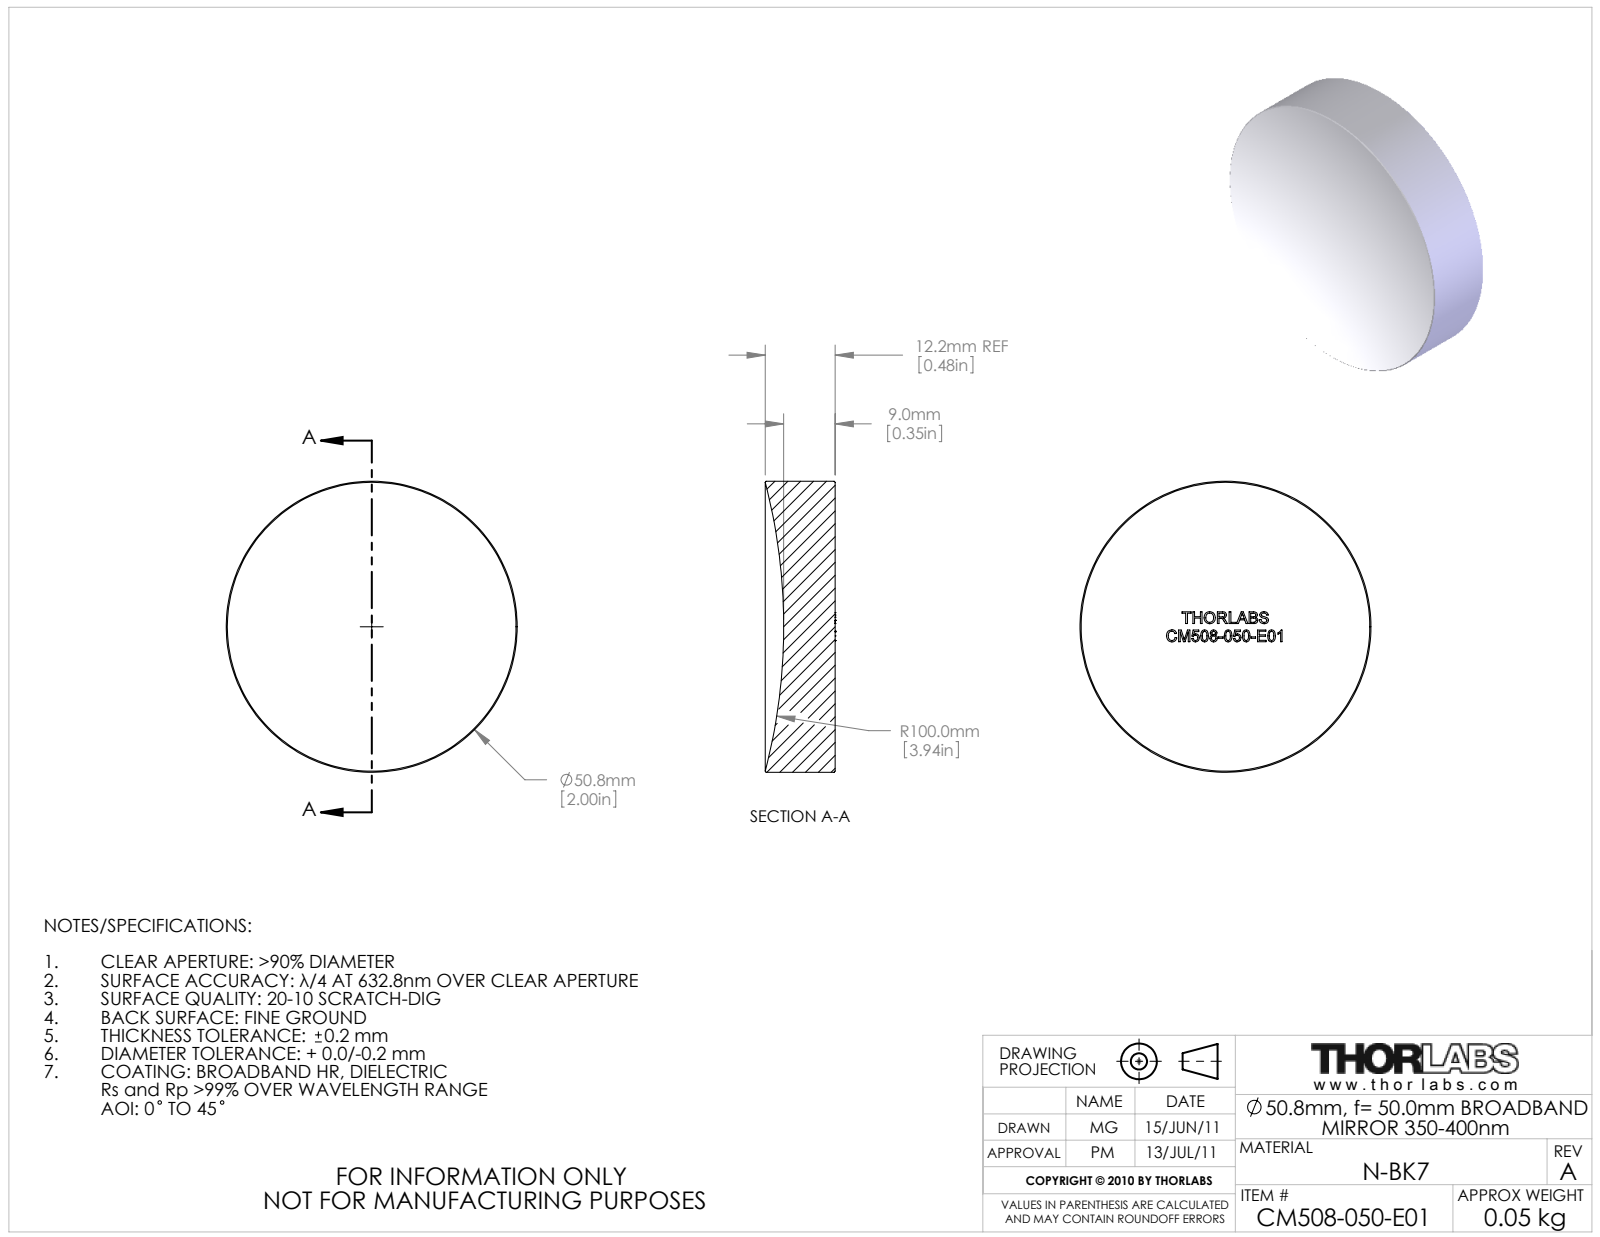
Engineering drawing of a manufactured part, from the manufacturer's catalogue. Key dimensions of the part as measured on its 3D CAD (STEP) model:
Part name (STEP PRODUCT): 22615-E0W
STEP written by: SolidWorks 2011 (AUTOMOTIVE_DESIGN)
Units: millimetres
Bodies: 0 solids, 43 faces (35 planar, 2 cylindrical, 6 other)
Overall size (bounding box): 50.8 × 50.8 × 12.23
Round bosses / shafts (diameter × count): ⌀50.8 ×1
Main face-to-face distances: 2.05
